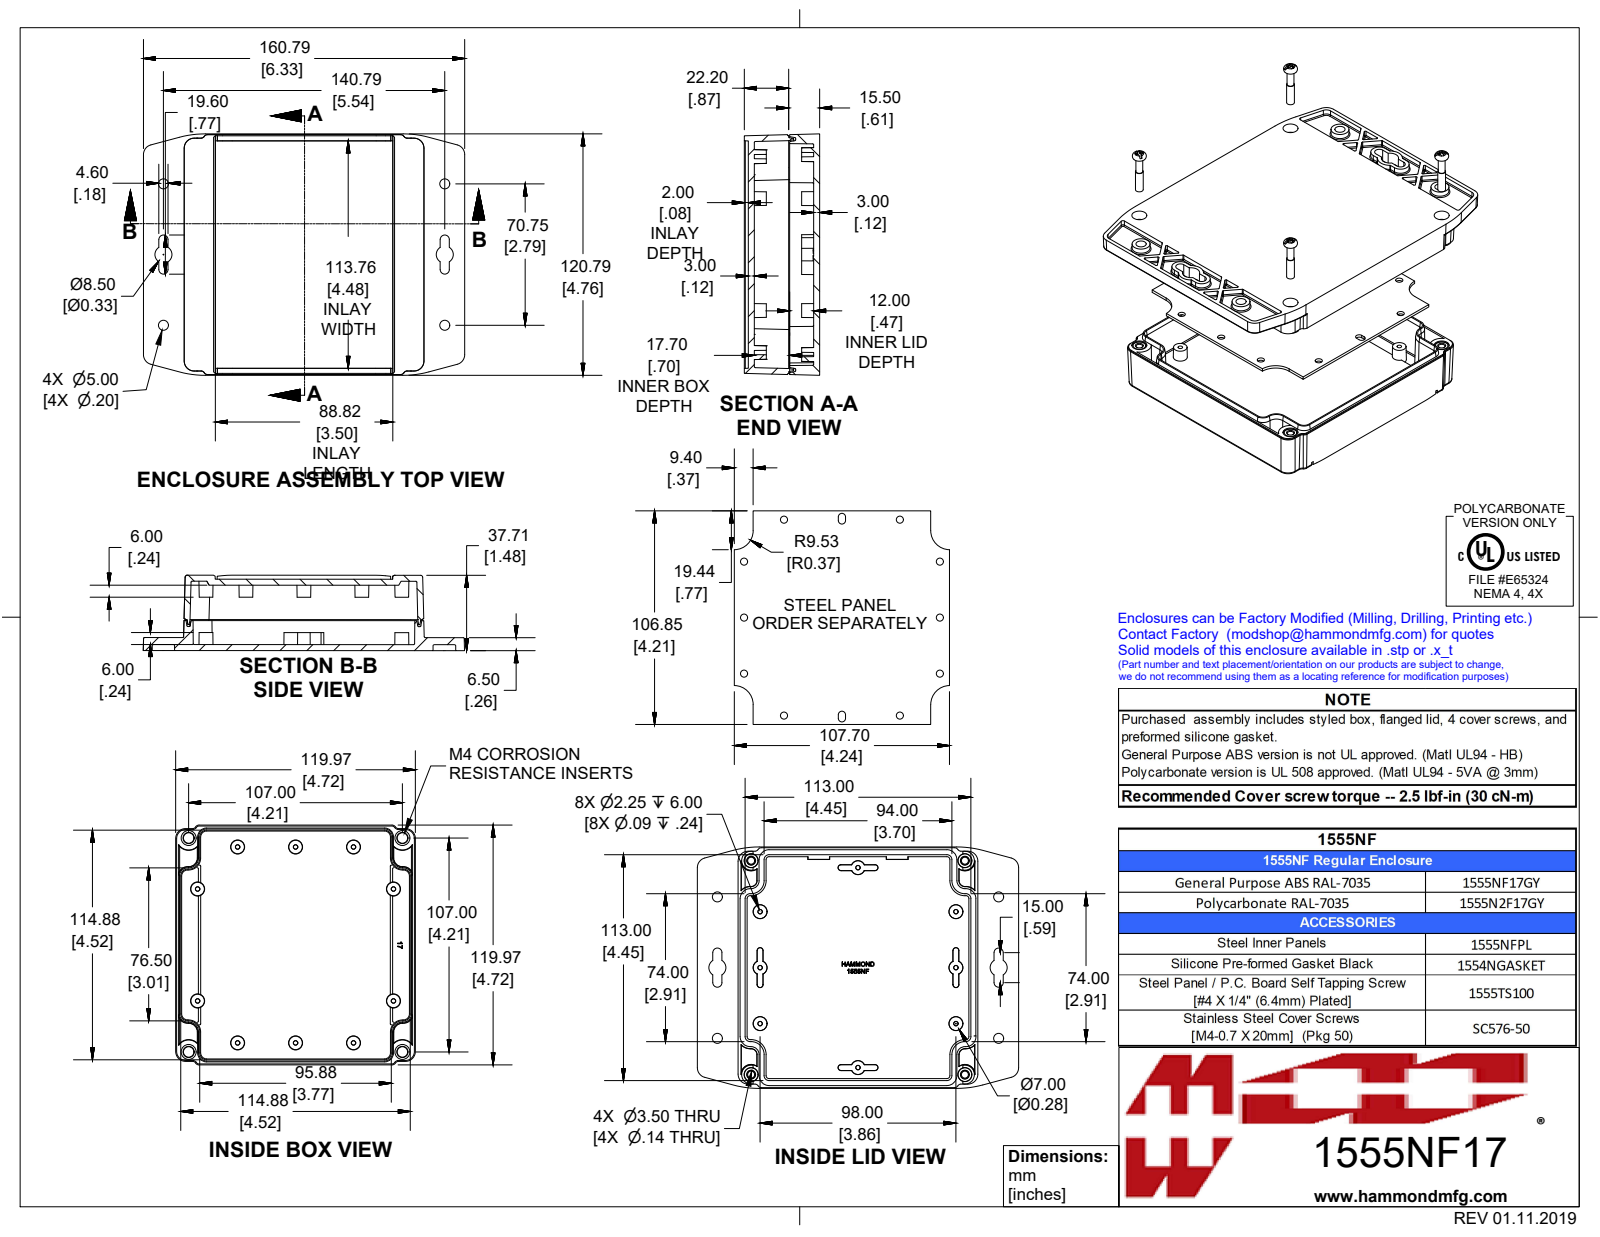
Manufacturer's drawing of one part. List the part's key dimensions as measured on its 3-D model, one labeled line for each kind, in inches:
Part name (STEP PRODUCT): 1555N2F17GY
STEP written by: SolidWorks 2019 (CONFIG_CONTROL_DESIGN)
Units: inches
Bodies: 11 solids, 1389 faces (608 planar, 301 cylindrical, 480 other)
Overall size (bounding box): 6.33 × 4.755 × 1.484
Volume: 11.41 in³ · Surface area: 217.5 in²
Round holes (diameter × count): ⌀0.141 ×10, ⌀0.128 ×4, ⌀0.138 ×4, ⌀0.295 ×4
Round bosses / shafts (diameter × count): ⌀0.354 ×4, ⌀0.25 ×4, ⌀0.218 ×4, ⌀0.21 ×4, ⌀0.153 ×4, ⌀0.135 ×4
Partial cylindrical surfaces — rounded edges, fillets, slot ends (radius × count): R0.02 ×140, R0.197 ×12, R0.039 ×10, R0.071 ×4, R0.089 ×4, R0.138 ×4, R0.169 ×4, R0.187 ×4
Main face-to-face distances: 0.118, 1.287, 0.236, 0.354, 0.933, 0.411, 0.293, 0.057, 1.169, 1.051
Hole centre spacings: 3.858, 0.981, 1.019, 1.102, 1.142, 2.083, 2.114, 3.132
